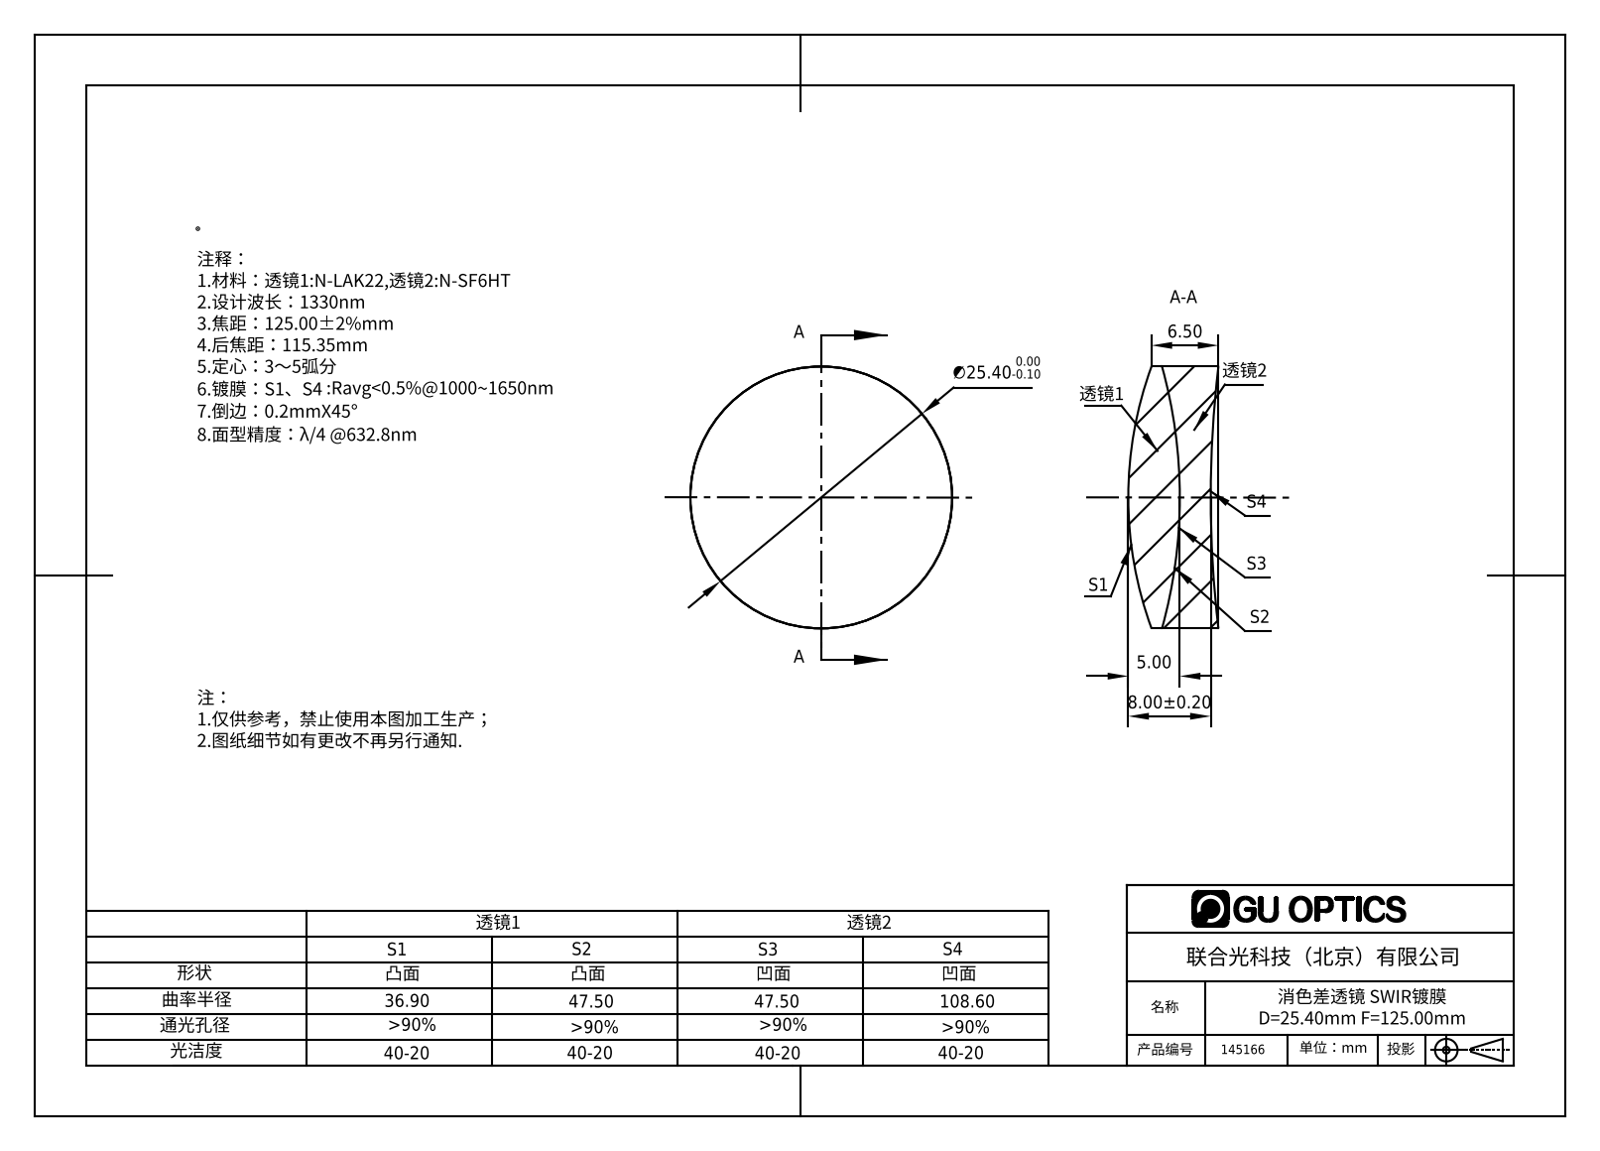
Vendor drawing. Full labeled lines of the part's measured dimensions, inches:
Part name (STEP PRODUCT): 145166
STEP written by: SolidWorks 2016 (AUTOMOTIVE_DESIGN)
Units: inches
Bodies: 2 solids, 12 faces (0 planar, 4 cylindrical, 8 other)
Overall size (bounding box): 1 × 1 × 0.344
Volume: 0.224 in³ · Surface area: 4.001 in²
Round bosses / shafts (diameter × count): ⌀1 ×1
